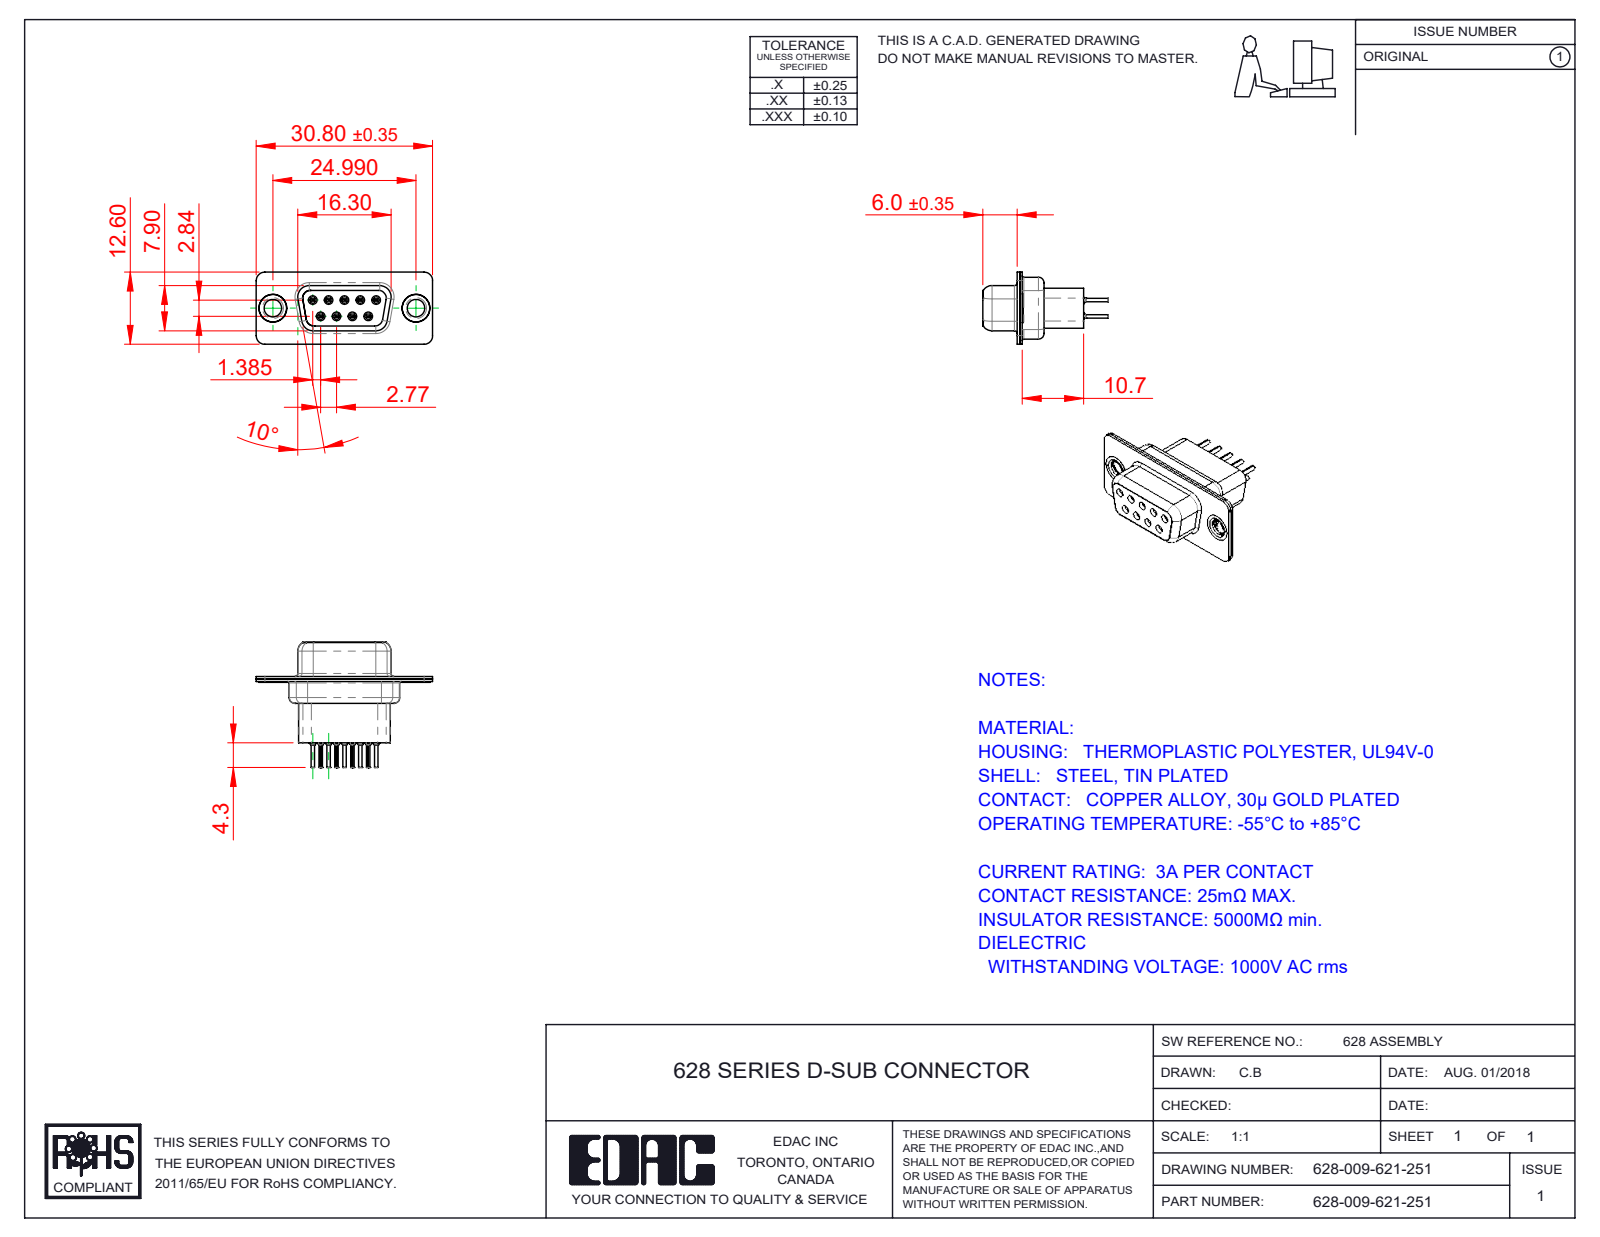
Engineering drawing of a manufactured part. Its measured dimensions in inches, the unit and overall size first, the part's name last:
Units: inches
Overall size (bounding box): 1.213 × 0.862 × 0.496
Round holes (diameter × count): ⌀0.008 ×9, ⌀0.031 ×9, ⌀0.035 ×9, ⌀0.043 ×9, ⌀0.063 ×9, ⌀0.067 ×5, ⌀0.12 ×2, ⌀0.157 ×2, ⌀0.159 ×2, ⌀0.191 ×2
Round bosses / shafts (diameter × count): ⌀0.079 ×9, ⌀0.059 ×9, ⌀0.047 ×9, ⌀0.024 ×9, ⌀0.197 ×2, ⌀0.195 ×2, ⌀0.189 ×2, ⌀0.14 ×2
Partial cylindrical surfaces — rounded edges, fillets, slot ends (radius × count): R0.004 ×18, R0.059 ×17, R0.079 ×12, R0.011 ×9, R0.053 ×6, R0.01 ×4, R0.02 ×4, R0.024 ×4
Main face-to-face distances: 0.018, 0.016, 0.035, 0.335, 0.26, 0.075, 0.055, 0.276, 0.278, 0.02
Hole centre spacings: 0.124, 0.109, 0.218, 0.198, 0.198, 0.327, 0.294, 0.295
Volume: 0.131 in³ · Surface area: 8.045 in²
Bodies: 14 solids, 1360 faces (346 planar, 418 cylindrical, 596 other)
Part name (STEP PRODUCT): 628 Shell Rear_09 Contacts; 628 Shell Front_09 Contacts; 628-009-621-251; 628 Contact Row 1_21H (+3 more)
STEP written by: SolidWorks 2020 (CONFIG_CONTROL_DESIGN)
